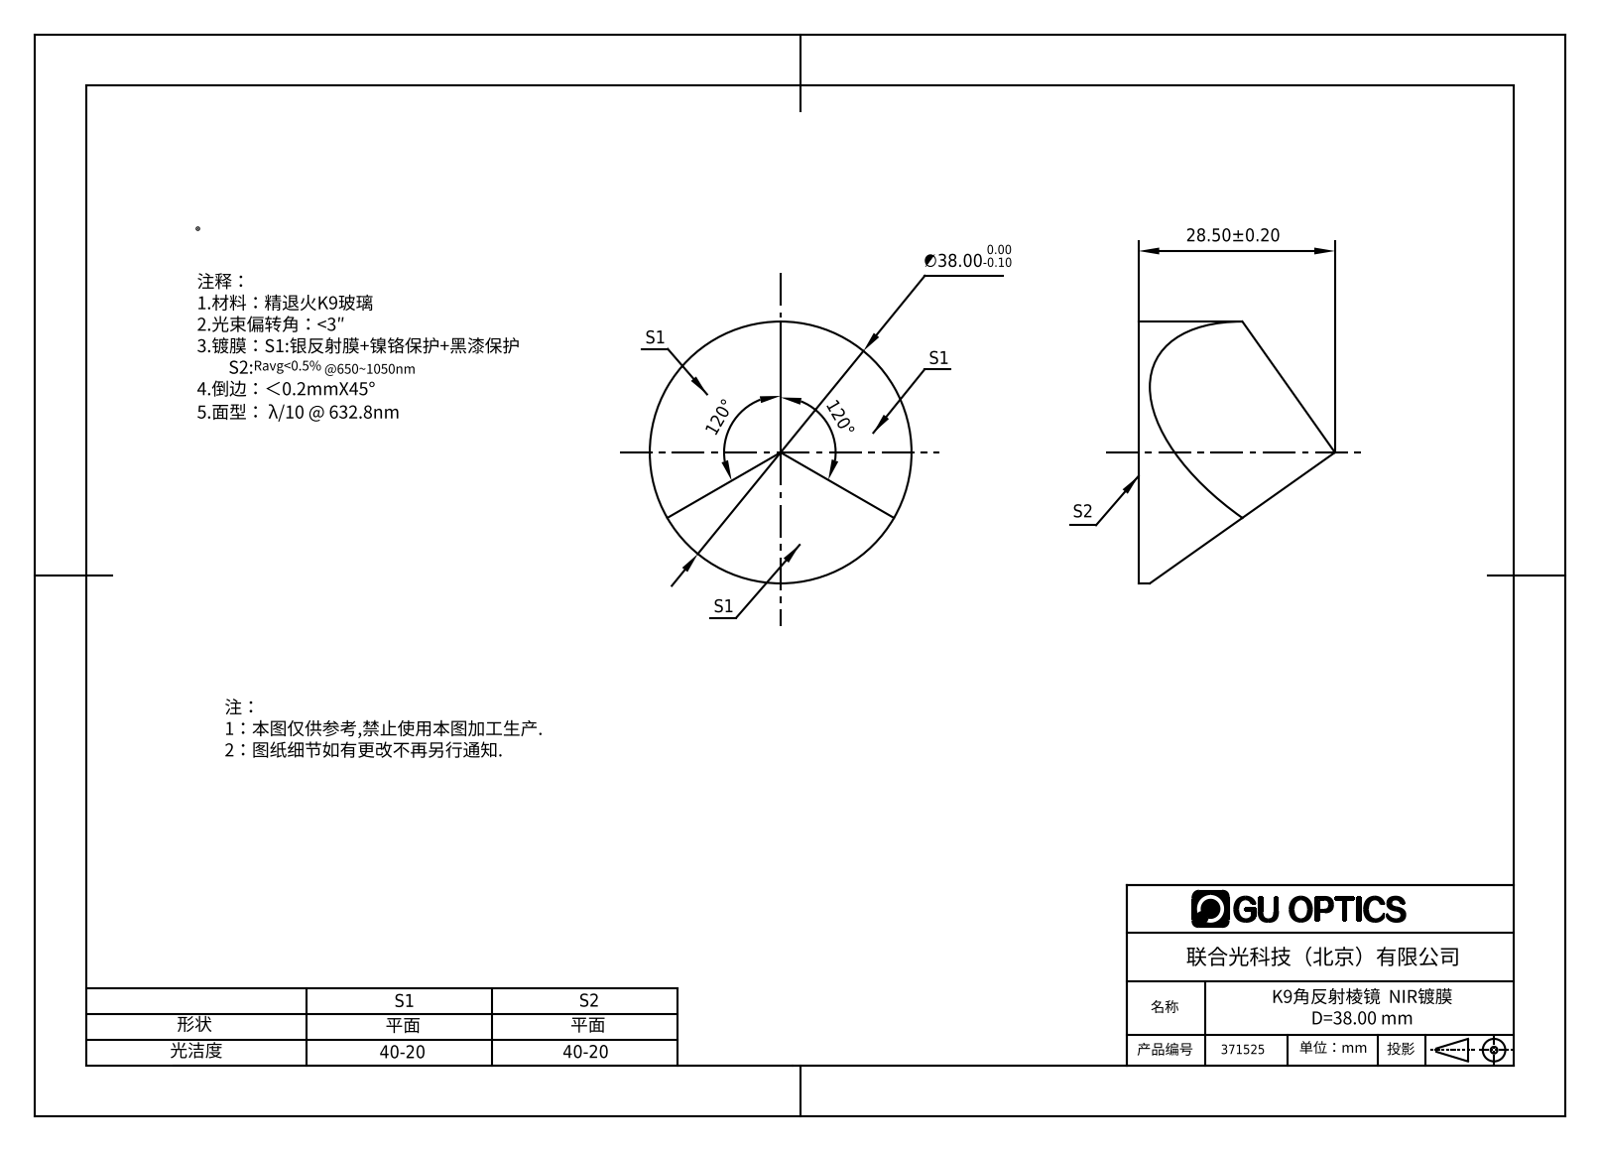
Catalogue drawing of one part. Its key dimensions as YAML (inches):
part_name: "371505"
step_written_by: "SolidWorks 2016 (CONFIG_CONTROL_DESIGN)"
units: inches
bodies: {solids: 1, faces: 6, planar: 4, cylindrical: 2, other: 0}
overall_size: [1.496, 1.496, 1.122]
volume: 0.947
surface_area: 5.964
round_bosses_or_shafts:
  - {diameter: 1.496, count: 1}
